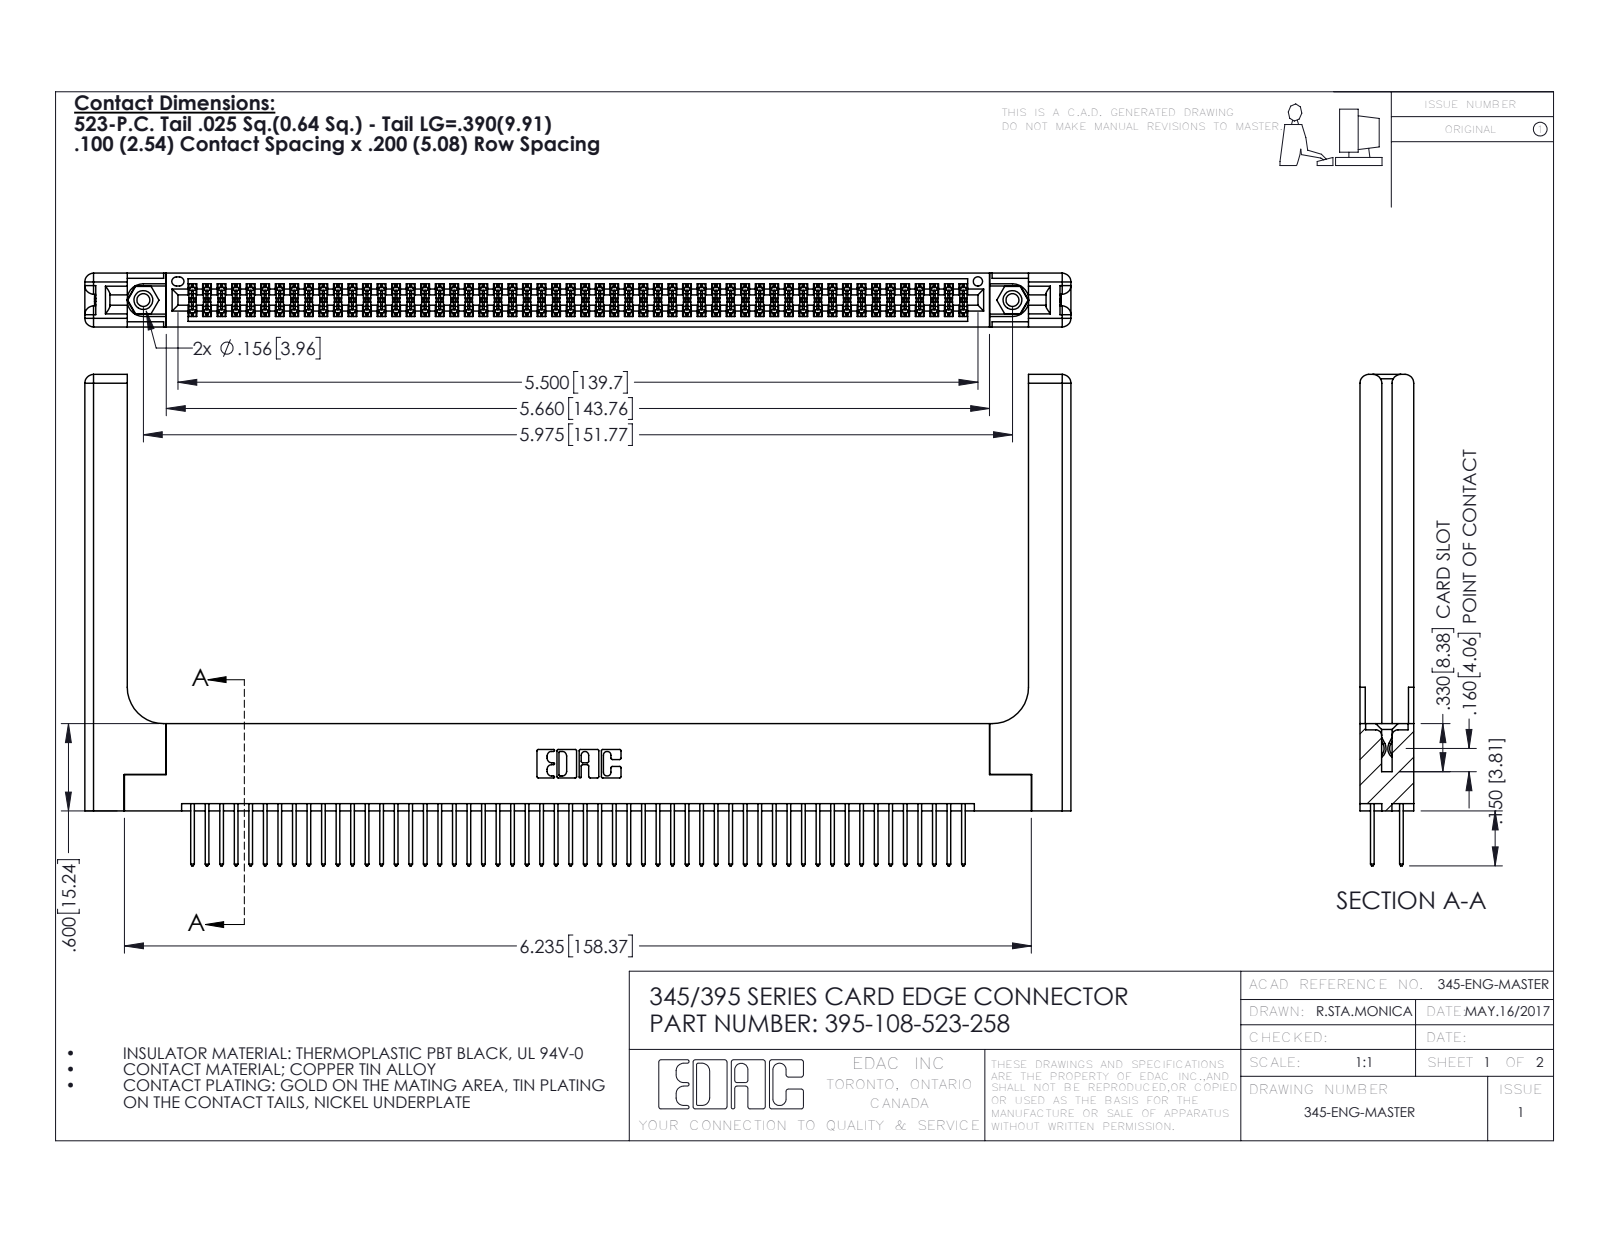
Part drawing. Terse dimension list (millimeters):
name: 345-292-001_345-293-123; 345-220-058_345-220-058; 345 Part_Flush Mounting Lugs - 0.156 Dia-TH; 395-108-523-258 (+1 more)
written by: SolidWorks 2016 (CONFIG_CONTROL_DESIGN)
unit: mm
bodies: 113 solids, 5782 faces (3792 planar, 1930 cylindrical, 60 other)
size: 172.2 × 85.8 × 9.4
volume: 25 530 mm³; area: 31 500 mm²
holes: 2× ⌀2.3, 2× ⌀3.2, 2× ⌀4, 1× ⌀1.6
bosses: 2× ⌀3.9
rounds: 162× R0.2, 108× R0.3, 22× R0.3, 16× R1.5, 6× R0.2, 6× R0.8, 3× R0.7, 2× R0.4
face distances: 1.8, 7.6, 9.4, 5.1, 2.5, 6.9, 0.6, 5.7, 4.4, 3.8
hole spacings: 6.9, 145.8, 151.8
